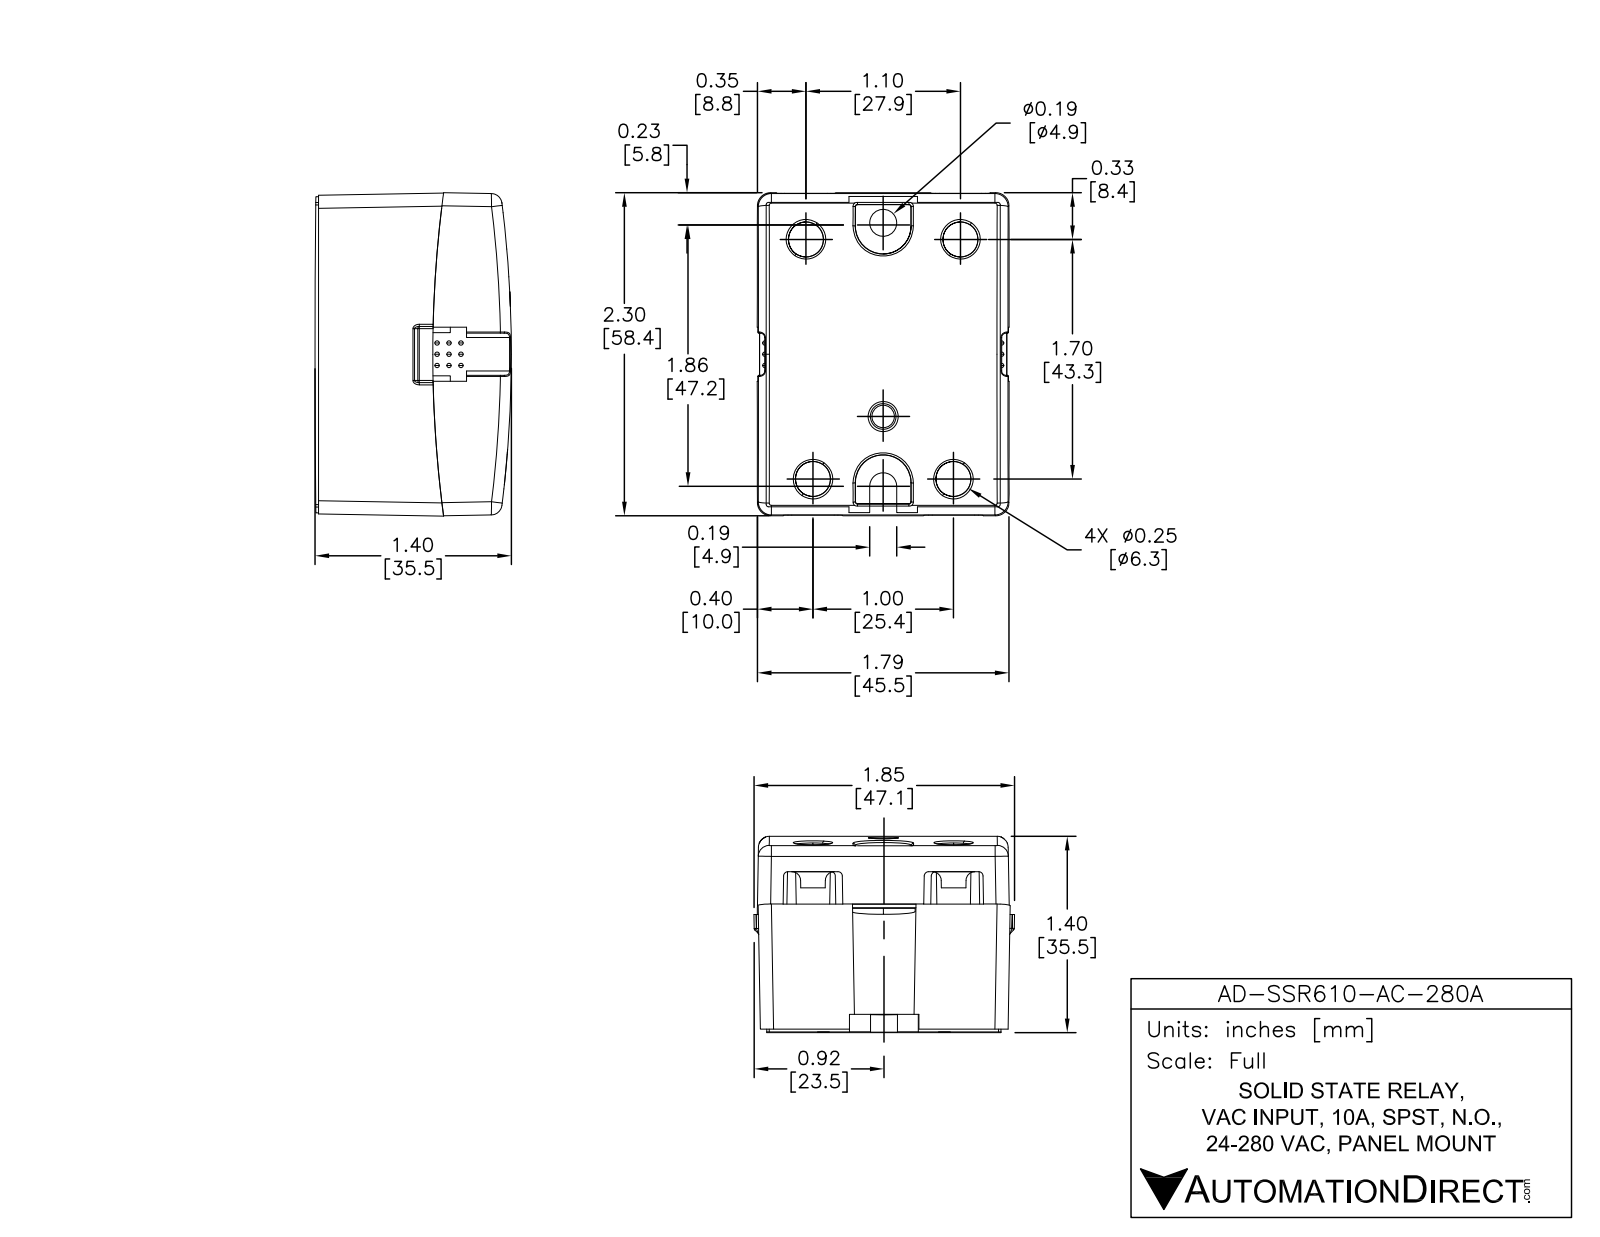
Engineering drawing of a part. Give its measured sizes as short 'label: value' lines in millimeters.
name: AD-SSR610-AC-280A
written by: SolidWorks 2013 (AUTOMOTIVE_DESIGN)
unit: mm
bodies: 3 solids, 251 faces (145 planar, 95 cylindrical, 11 other)
size: 58.4 × 45.5 × 35.6
volume: 84 230 mm³; area: 17 040 mm²
holes: 4× ⌀6.4, 1× ⌀4.8
bosses: 2× ⌀10.2, 2× ⌀8.9, 2× ⌀7.6, 2× ⌀6.4, 2× ⌀5.1, 2× ⌀5.1
rounds: 6× R0.8, 4× R0.3, 4× R1, 4× R12.7, 2× R4.9, 1× R2.4, 1× R12.7, 1× R12.7
face distances: 45.5, 58.4, 29.6, 6.4, 23.3, 17, 26.9, 12.7, 45.7, 2
hole spacings: 14.1, 14.4, 25.4, 27.9, 43.2, 43.2, 47.7, 47.7
